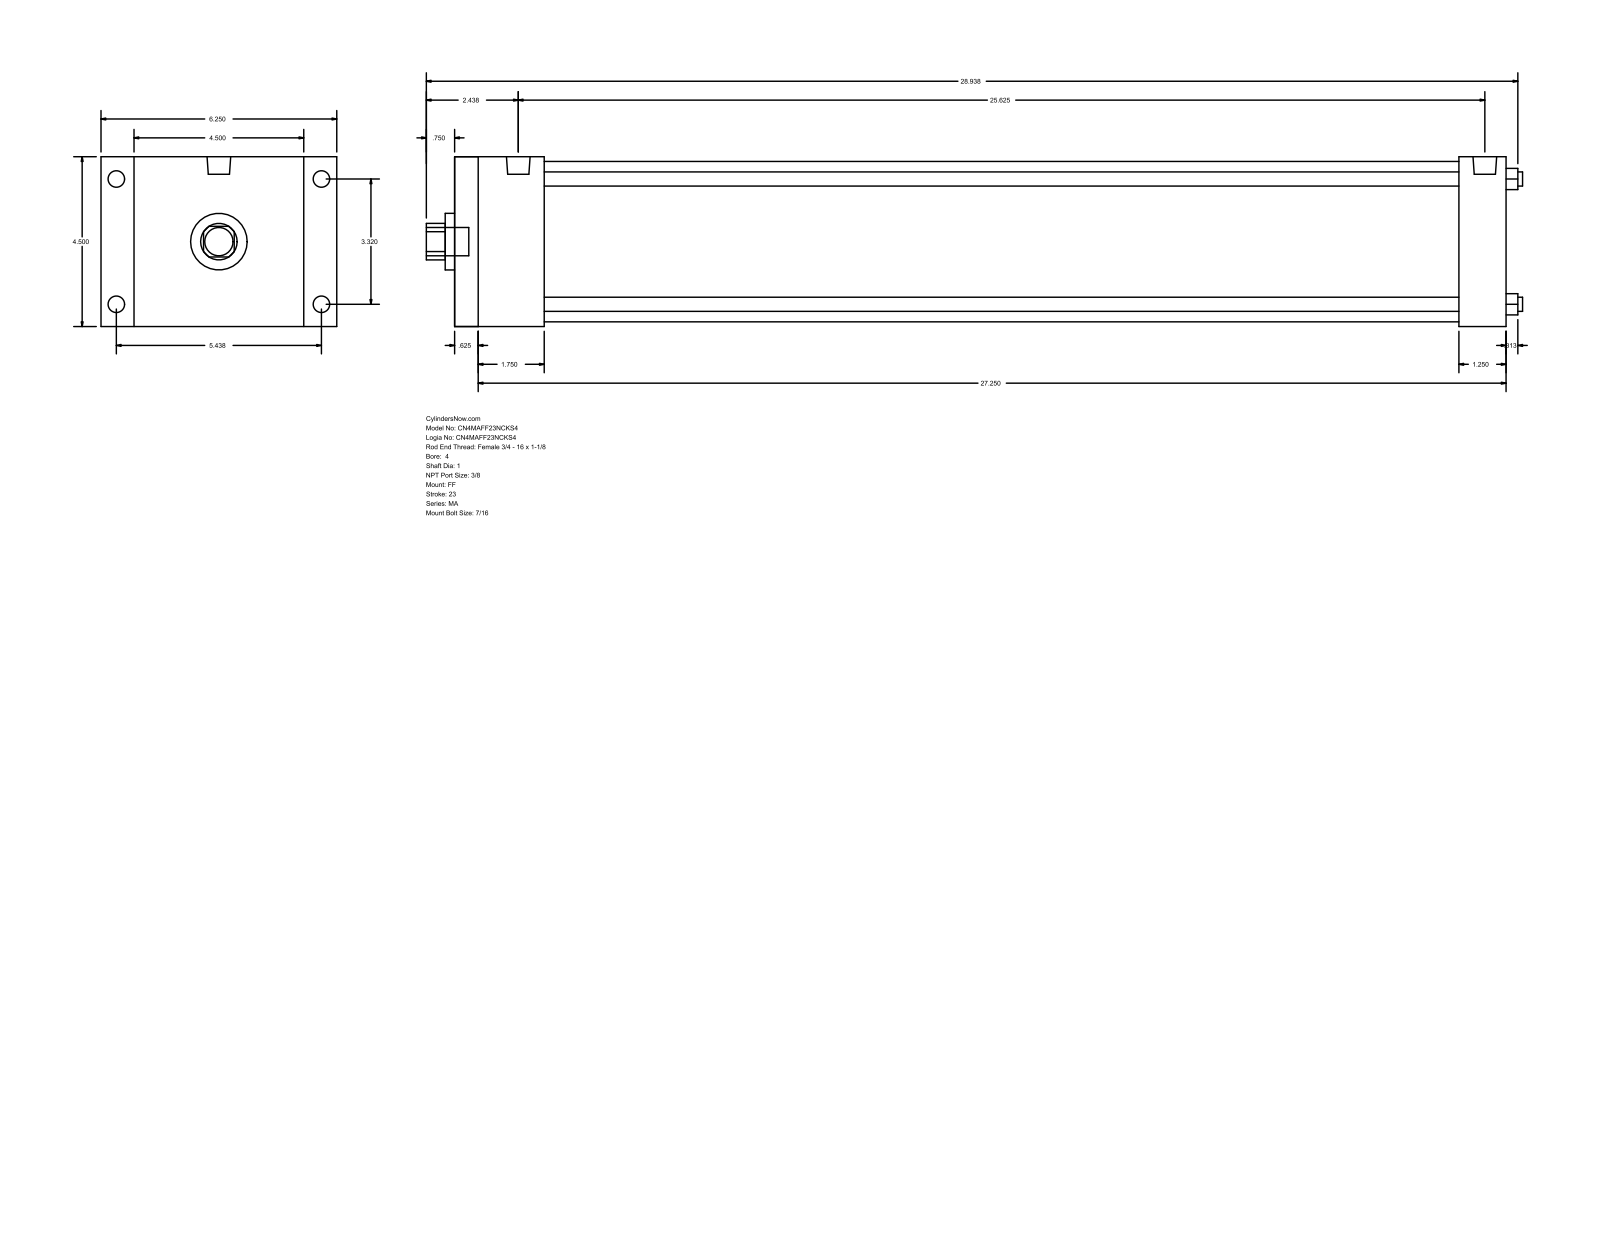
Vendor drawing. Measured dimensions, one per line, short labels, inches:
name: MA_FF__0400_1
written by: GSSL Pune (CONFIG_CONTROL_DESIGN)
unit: in
bodies: 0 solids, 92 faces (64 planar, 28 cylindrical, 0 other)
size: 29.063 × 6.25 × 4.5
holes: 4× ⌀0.375, 1× ⌀1, 1× ⌀1.5, 1× ⌀4.25
bosses: 8× ⌀0.437, 2× ⌀0.627, 1× ⌀0.75
rounds: 1× R0.484
face distances: 4.5, 27.875, 0.625, 27.25, 0.875, 5.375, 26.625, 26, 1.25, 2.375
hole spacings: 2.347, 3.32, 4.695
